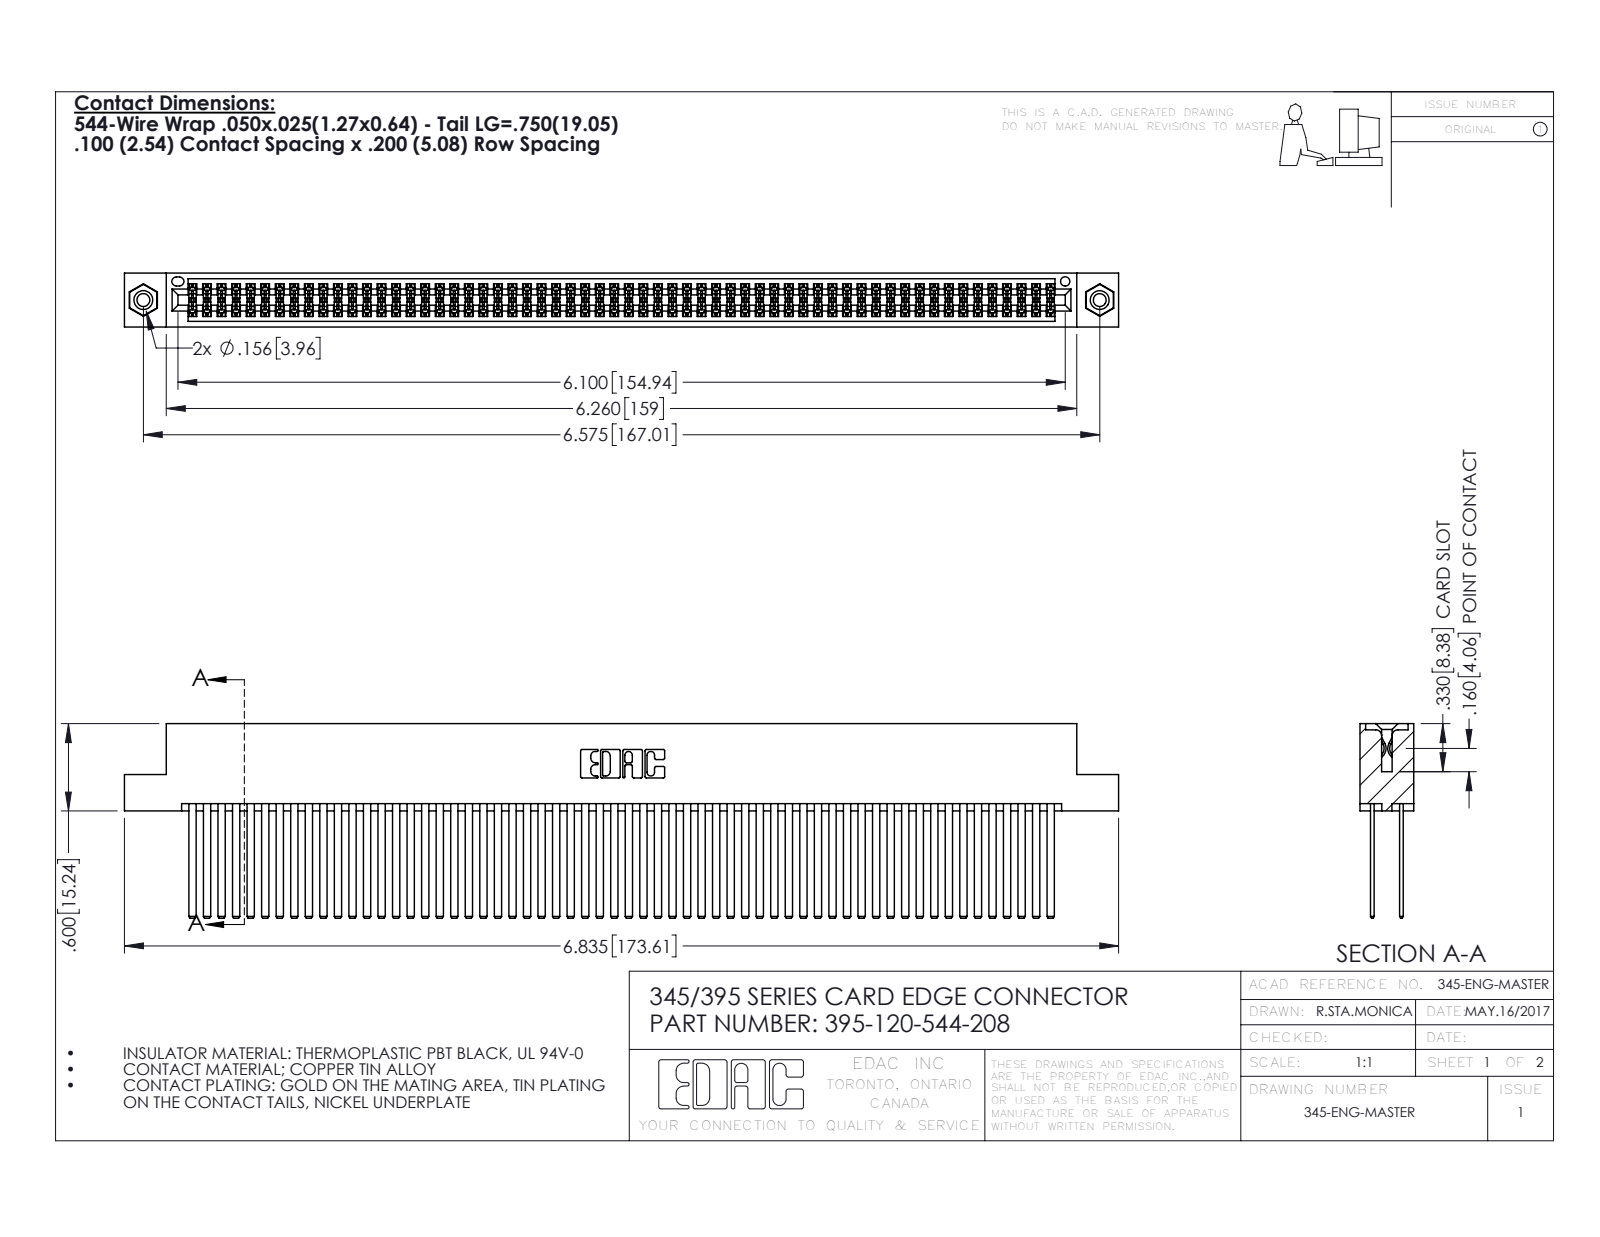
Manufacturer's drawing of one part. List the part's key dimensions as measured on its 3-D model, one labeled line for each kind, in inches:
Part name (STEP PRODUCT): 395-120-544-208; 345 Part_Flush Mounting Lugs - 0.156 Dia-TI; 345-292-001_345-293-144; 345-250-001_345-250-003-102
STEP written by: SolidWorks 2016 (CONFIG_CONTROL_DESIGN)
Units: inches
Bodies: 123 solids, 5466 faces (3592 planar, 1858 cylindrical, 16 other)
Overall size (bounding box): 6.835 × 1.337 × 0.37
Volume: 1.142 in³ · Surface area: 51.06 in²
Round holes (diameter × count): ⌀0.089 ×2, ⌀0.125 ×2, ⌀0.156 ×2, ⌀0.064 ×1
Round bosses / shafts (diameter × count): ⌀0.155 ×2
Partial cylindrical surfaces — rounded edges, fillets, slot ends (radius × count): R0.006 ×180, R0.01 ×22, R0.007 ×6, R0.031 ×6, R0.026 ×3, R0.014 ×2, R0.019 ×2, R0.022 ×2
Main face-to-face distances: 0.2, 0.025, 0.072, 0.098, 0.272, 0.298, 0.225, 0.175, 0.37, 0.05
Hole centre spacings: 0.27, 6.339, 6.575
